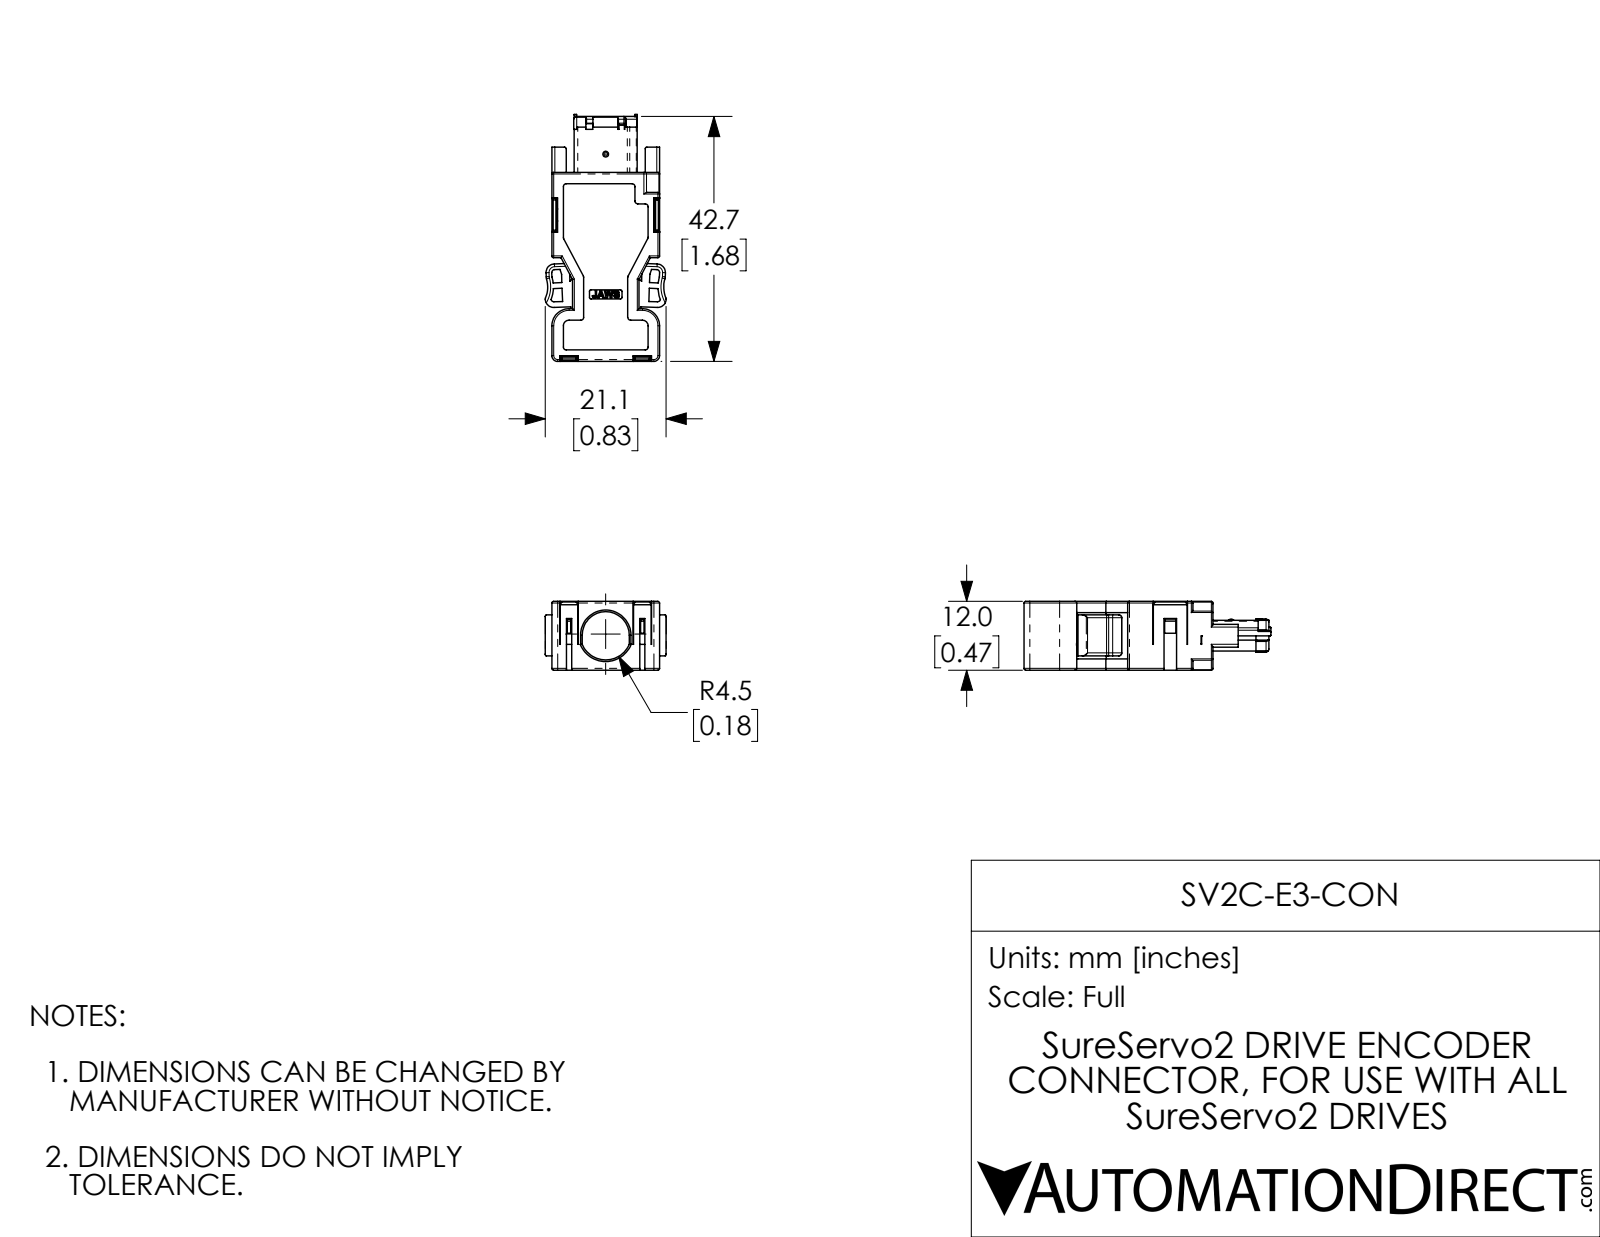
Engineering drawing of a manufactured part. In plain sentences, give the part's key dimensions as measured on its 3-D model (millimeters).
The part is named "IEEE1394 Shell Only 1 Ext fil". Its 3-D file was written by "SolidWorks 2017 (AUTOMOTIVE_DESIGN)". It is 1 solid with 767 faces: 482 planar, 162 cylindrical and 123 other. Overall it measures 43.1 by 21.11 by 12 millimeters. Its volume is 7 255 cubic millimeters and its surface area 4 198 square millimeters. Partial cylindrical surfaces (rounded edges, fillets, slot ends): 42 of radius 0.3, 42 of radius 0.5, 8 of radius 0.1, 6 of radius 1.5, 4 of radius 0.6, 4 of radius 1, 3 of radius 0.2, 2 of radius 3. The main face-to-face distances are 11.6, 11.8, 1, 18.8, 12, 3.3, 17.8, 0.9, 14.9, 0.7.
